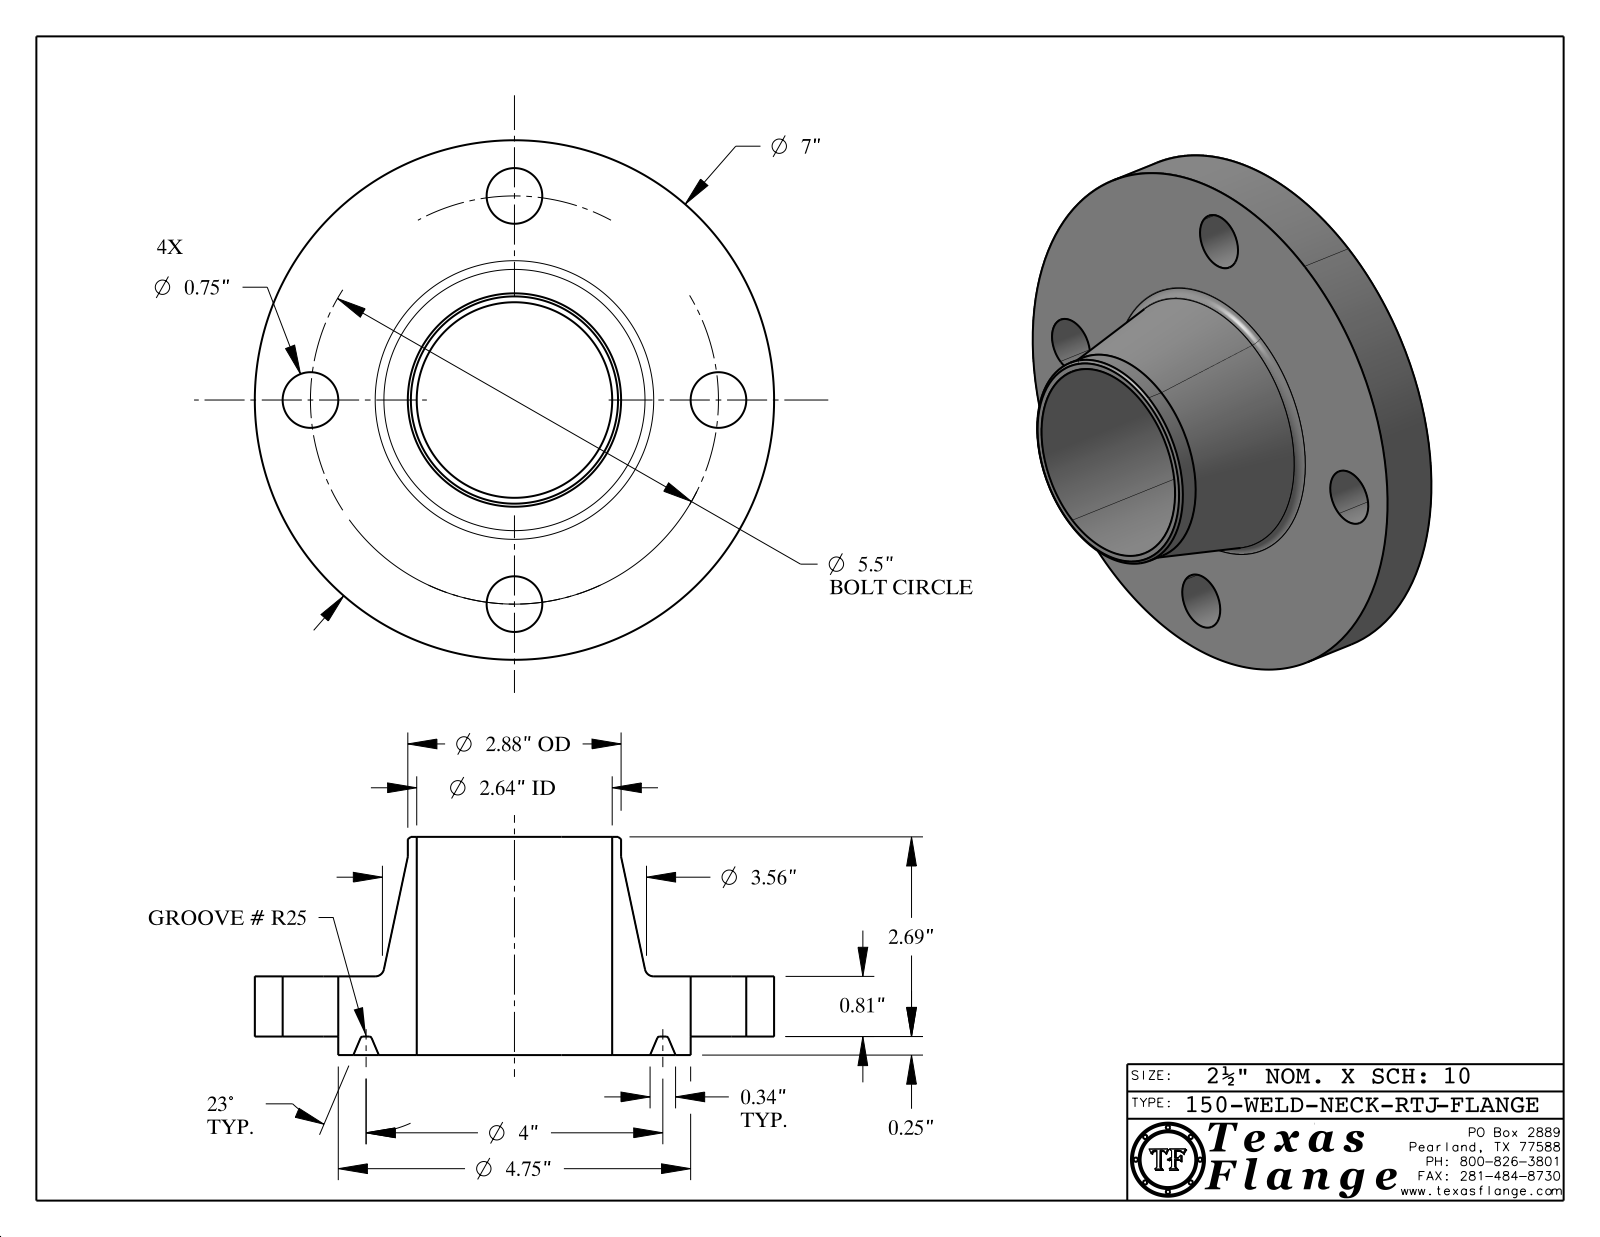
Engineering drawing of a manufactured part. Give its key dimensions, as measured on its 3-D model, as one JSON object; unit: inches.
{"part_name": "150-WELD-NECK-RTJ", "step_written_by": "CATIA V5 STEP AP214 (AUTOMOTIVE_DESIGN)", "units": "inches", "bodies": {"solids": 1, "faces": 421, "planar": 371, "cylindrical": 36, "other": 14}, "overall_size": [7, 7, 2.94], "volume_in3": 32.31, "surface_area_in2": 135.2, "round_holes": [[0.75, 4], [0.495, 1], [2.635, 1]], "round_bosses_or_shafts": [[0.03, 8], [7, 1], [4.75, 1], [2.875, 1], [0.39, 1]], "face_to_face_distances": [0.81, 0.25, 1.06, 2.94, 2.69, 1.88, 1.055, 0.805, 1.885, 0.148], "hole_center_spacings": [2.75, 3.889, 2.105, 5.081, 5.5]}
